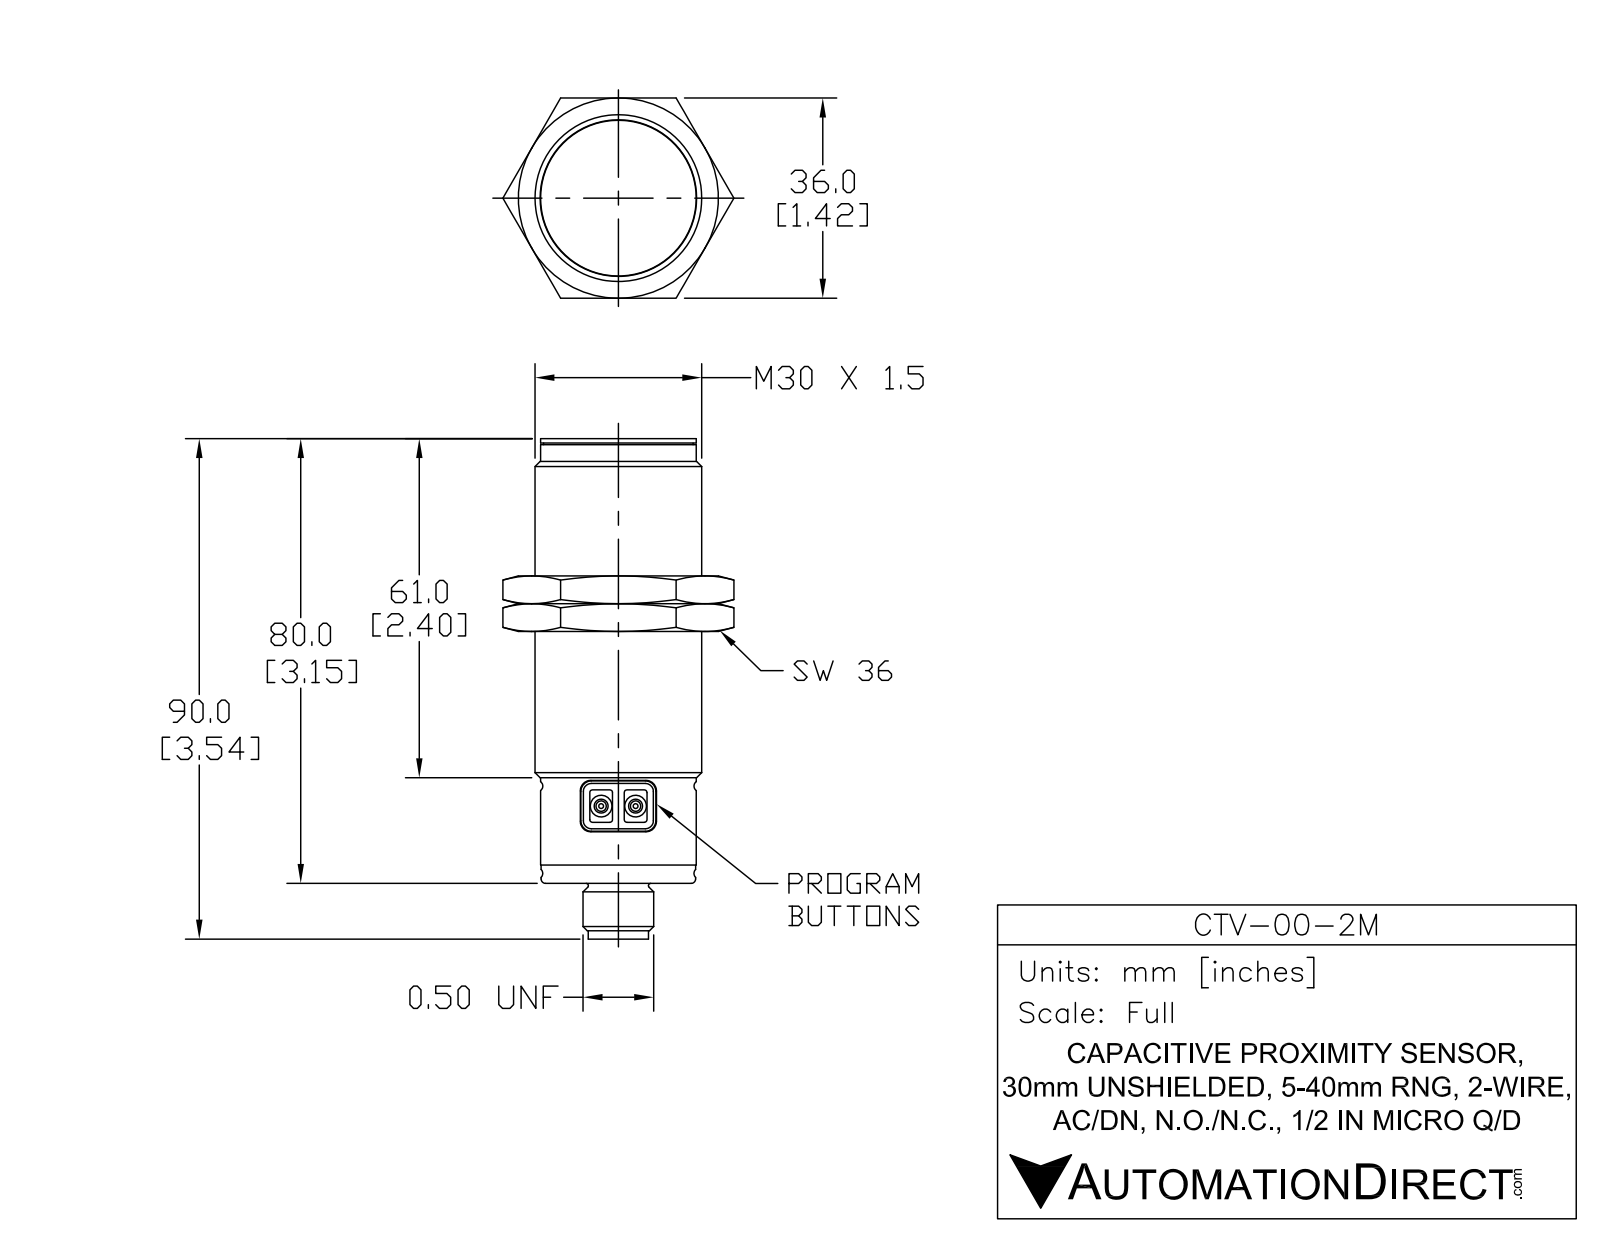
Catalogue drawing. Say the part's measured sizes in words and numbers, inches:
The part is named "CTV-00-2M". Its 3-D file was written by "SolidWorks 2017 (AUTOMOTIVE_DESIGN)". It is 3 solids with 167 faces: 55 planar, 48 cylindrical and 64 other. Overall it measures 3.531 by 1.637 by 1.417 inches. Its volume is 3.634 cubic inches and its surface area 20.61 square inches. Round holes: 1 of diameter 0.302, 1 of diameter 1.117. Round bosses or shafts: 2 of diameter 0.098, 1 of diameter 1.181, 1 of diameter 1.102, 1 of diameter 1.094, 1 of diameter 1.059, 1 of diameter 0.5, 1 of diameter 0.427. Partial cylindrical surfaces (rounded edges, fillets, slot ends): 8 of radius 0.02, 4 of radius 0.039, 4 of radius 0.075, 2 of radius 0.095, 1 of radius 0.008, 1 of radius 0.175. The main face-to-face distances are 1.169, 0.197, 1.417, 1.98, 3.15, 1.783, 1.366, 2.177, 0.394, 0.972.
